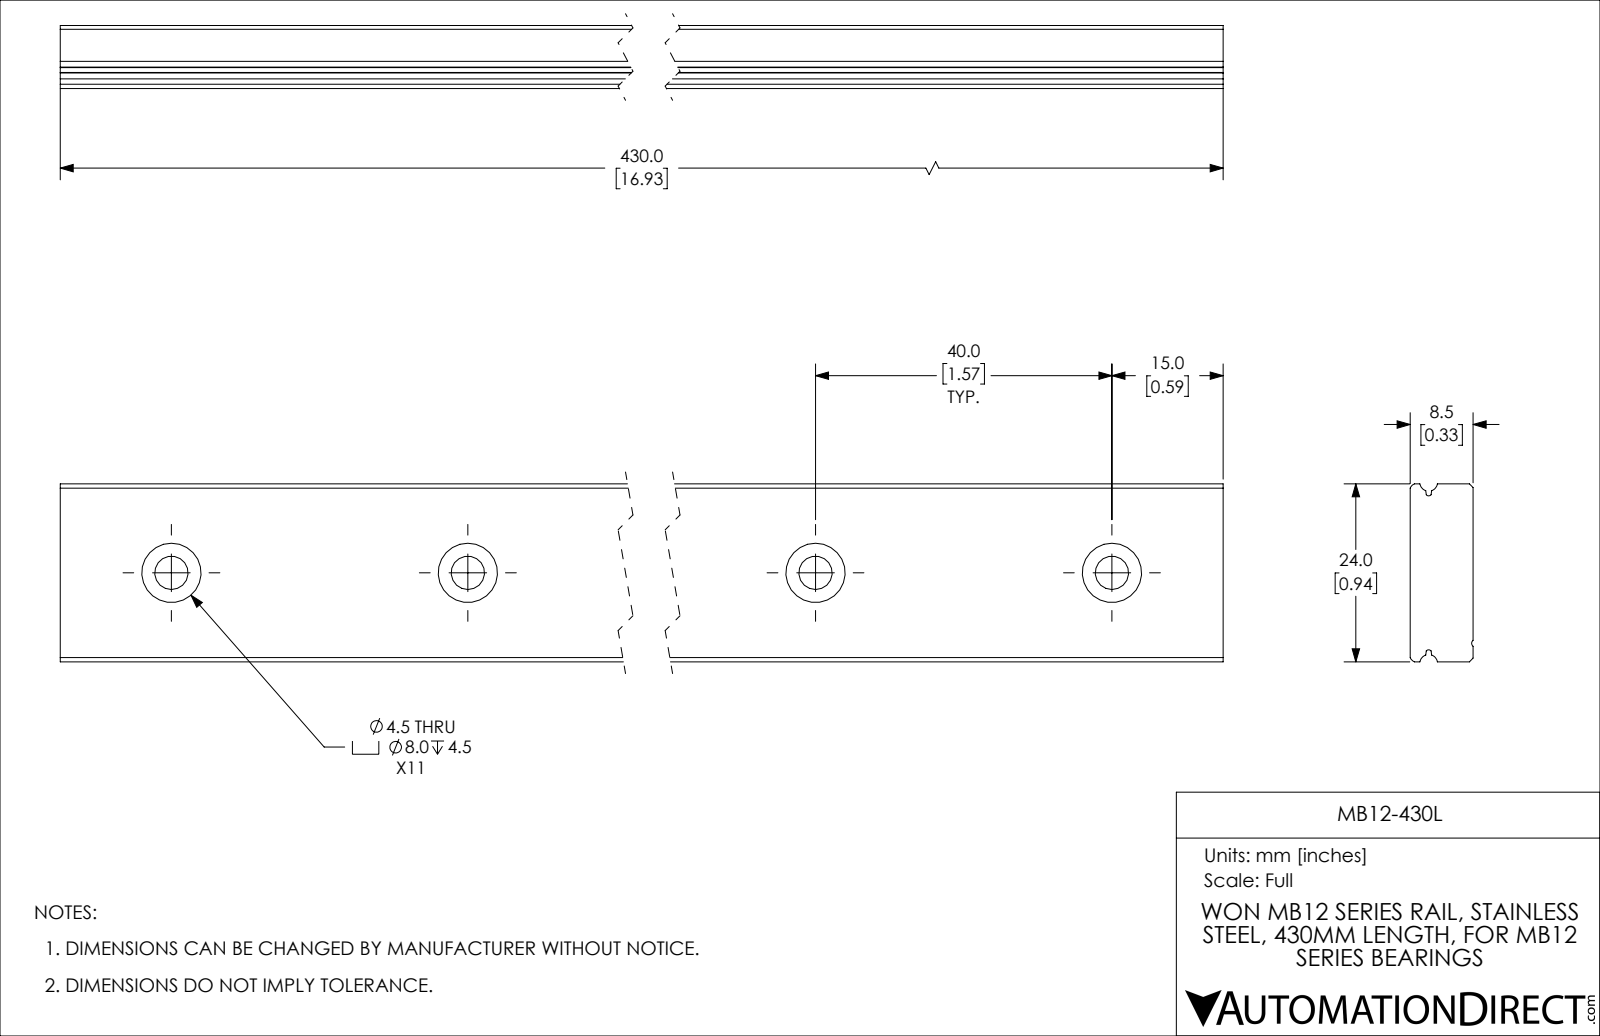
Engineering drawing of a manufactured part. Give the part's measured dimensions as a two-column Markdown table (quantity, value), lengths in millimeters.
| quantity | value |
| --- | --- |
| part name | MB12-430L |
| STEP written by | SolidWorks 2019 (CONFIG_CONTROL_DESIGN) |
| units | millimeters |
| bodies | 1 solid, 80 faces (26 planar, 54 cylindrical, 0 other) |
| overall size | 430 × 24 × 8.5 |
| volume | 82 394 mm³ |
| surface area | 31 124 mm² |
| round holes (diameter × count) | 4.5 × 11, 8 × 11 |
| partial cylindrical surfaces (radius × count) | 0.42 × 2, 1.15 × 2, 1.2 × 2, 0.5 × 1 |
| main face-to-face distances | 8.5, 24, 2.21, 4, 4.5, 430 |
| hole center spacings | 40, 80, 120, 160, 200, 240, 280, 320 |
